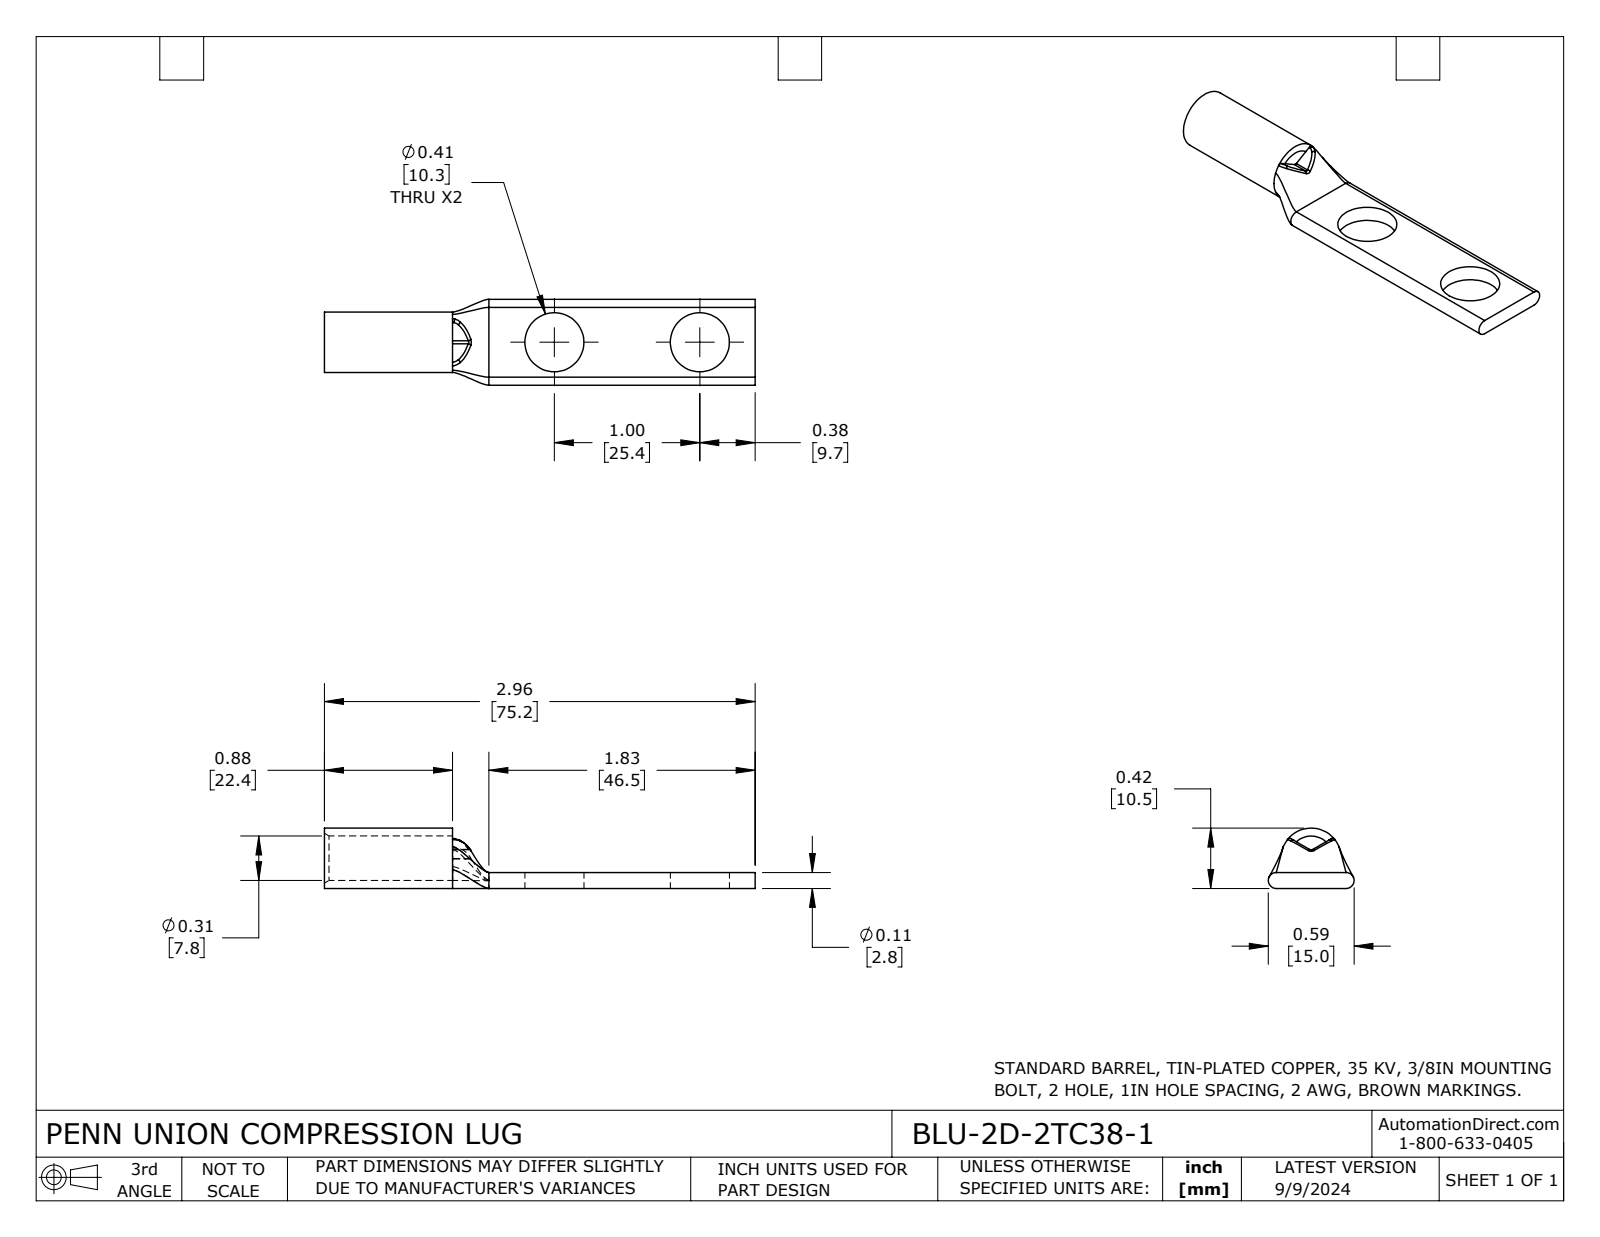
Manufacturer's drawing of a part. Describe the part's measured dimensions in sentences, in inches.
The part is named "BLU-2D-2TC38-1". Its 3-D file was written by "SolidWorks 2023 (CONFIG_CONTROL_DESIGN)". It is 1 solid with 40 faces: 11 planar, 13 cylindrical and 16 other. Overall it measures 2.96 by 0.59 by 0.415 inches. Its volume is 0.154 cubic inches and its surface area 4.927 square inches. Round holes: 2 of diameter 0.406, 1 of diameter 0.306. Round bosses or shafts: 1 of diameter 0.415. Partial cylindrical surfaces (rounded edges, fillets, slot ends): 2 of radius 0.02, 2 of radius 0.055. The main face-to-face distances are 0.11, 2.96, 0.88, 2.08, 0.054, 1.13, 0.25, 1.83. The hole center spacings are 1.
